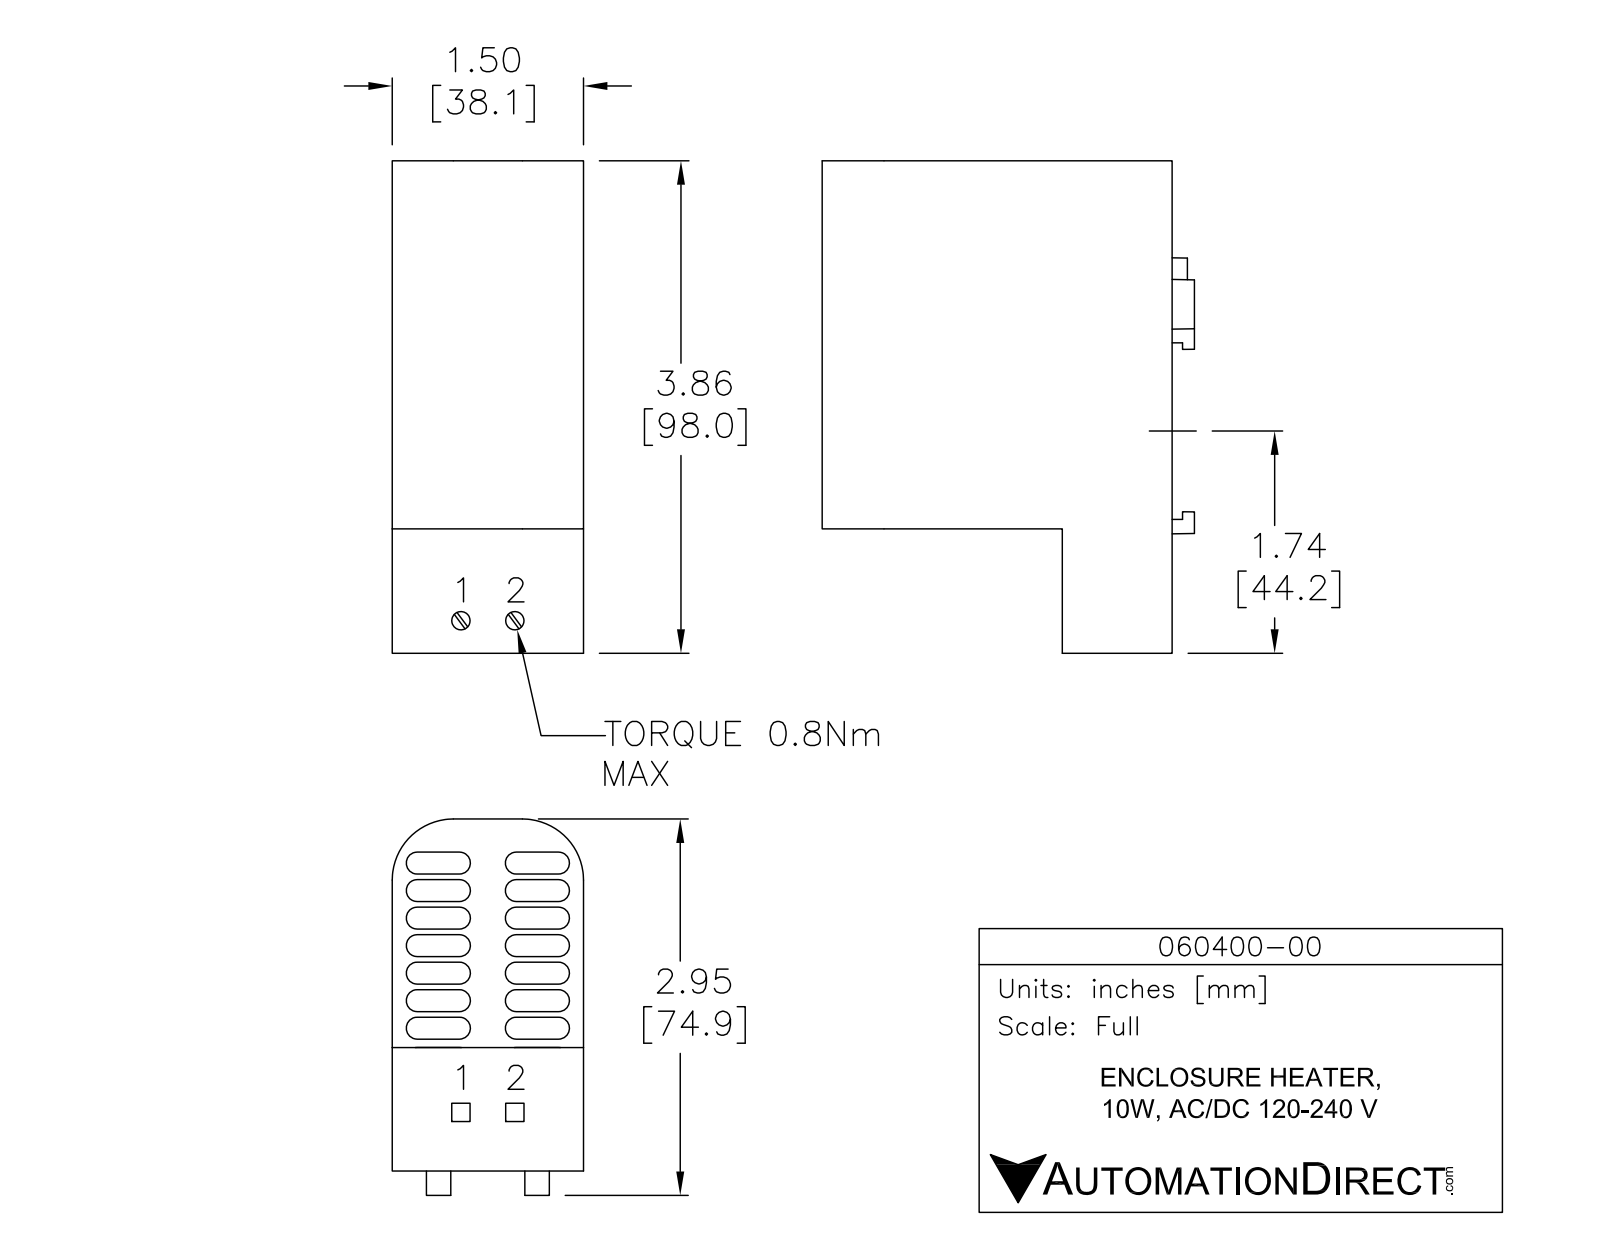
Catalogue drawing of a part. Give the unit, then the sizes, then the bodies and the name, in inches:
Units: inches
Overall size (bounding box): 3.86 × 3 × 1.5
Round holes (diameter × count): ⌀0.185 ×1, ⌀0.185 ×1
Partial cylindrical surfaces — rounded edges, fillets, slot ends (radius × count): R0.07 ×48, R0.06 ×6, R0.4 ×2
Main face-to-face distances: 0.03, 0.061, 1.491, 0.091, 1.461, 1.521, 0.42, 0.2, 2.695, 0.63
Hole centre spacings: 0.4
Volume: 12.4 in³ · Surface area: 52.67 in²
Bodies: 1 solid, 393 faces (279 planar, 108 cylindrical, 6 other)
Part name (STEP PRODUCT): 060400-00
STEP written by: SolidWorks 2013 (AUTOMOTIVE_DESIGN)
